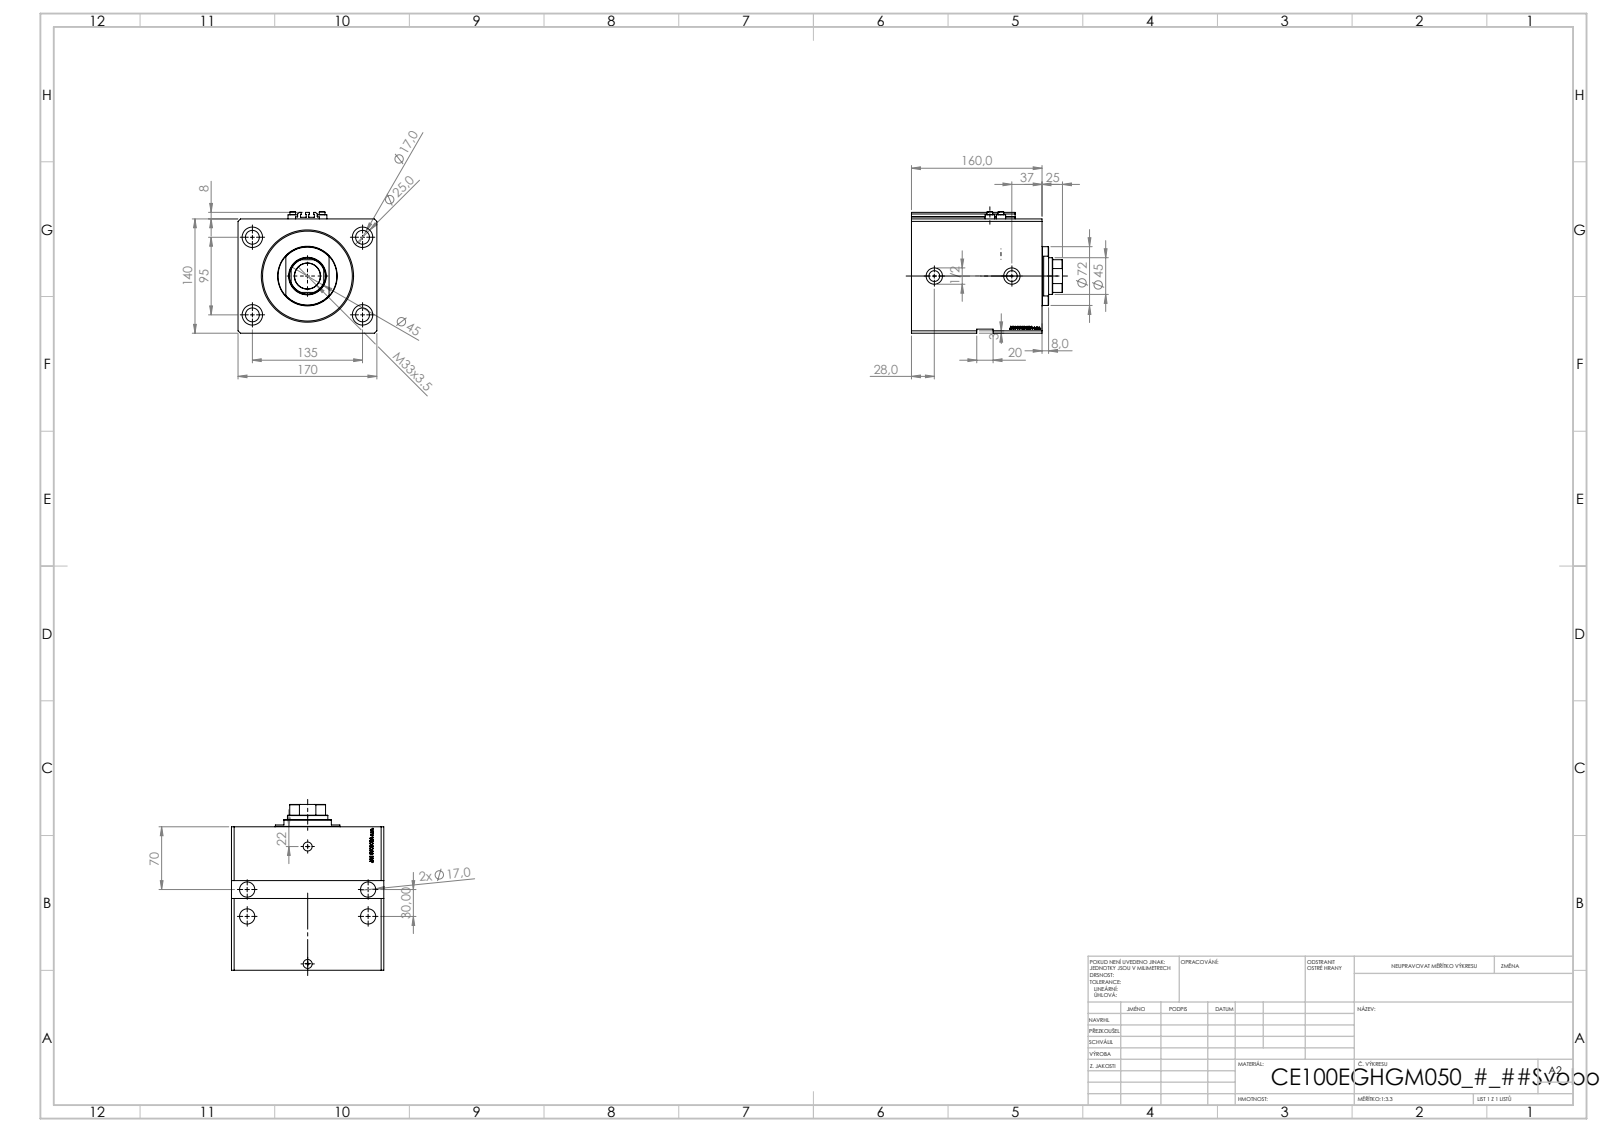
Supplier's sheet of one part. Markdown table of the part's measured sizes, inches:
| quantity | value |
| --- | --- |
| part name | V250CE_VC_E; V250CE_E_Body; ALLEN BOLT V250CE; V250CE_C_VCP |
| STEP written by | SolidWorks 2019 (CONFIG_CONTROL_DESIGN) |
| units | inches |
| bodies | 8 solids, 1123 faces (547 planar, 138 cylindrical, 438 other) |
| overall size | 7.283 × 6.693 × 5.866 |
| volume | 197.1 in³ |
| surface area | 533.2 in² |
| round holes (diameter × count) | 0.669 × 8, 0.049 × 4, 0.157 × 4, 0.984 × 4, 0.394 × 2, 0.518 × 2, 0.787 × 2, 1.24 × 1, 1.772 × 1, 3.937 × 1, 4.449 × 1 |
| round bosses / shafts (diameter × count) | 0.457 × 4, 0.276 × 4, 2.835 × 1 |
| partial cylindrical surfaces (radius × count) | 0.008 × 10, 0.866 × 1 |
| main face-to-face distances | 5.512, 6.693, 6.299, 1.138, 5.161, 5.315, 0.984, 4.177, 1.969, 3.346 |
| hole center spacings | 3.25, 5.315, 3.74, 0.535, 1.181, 1.324, 1.417, 1.515 |
